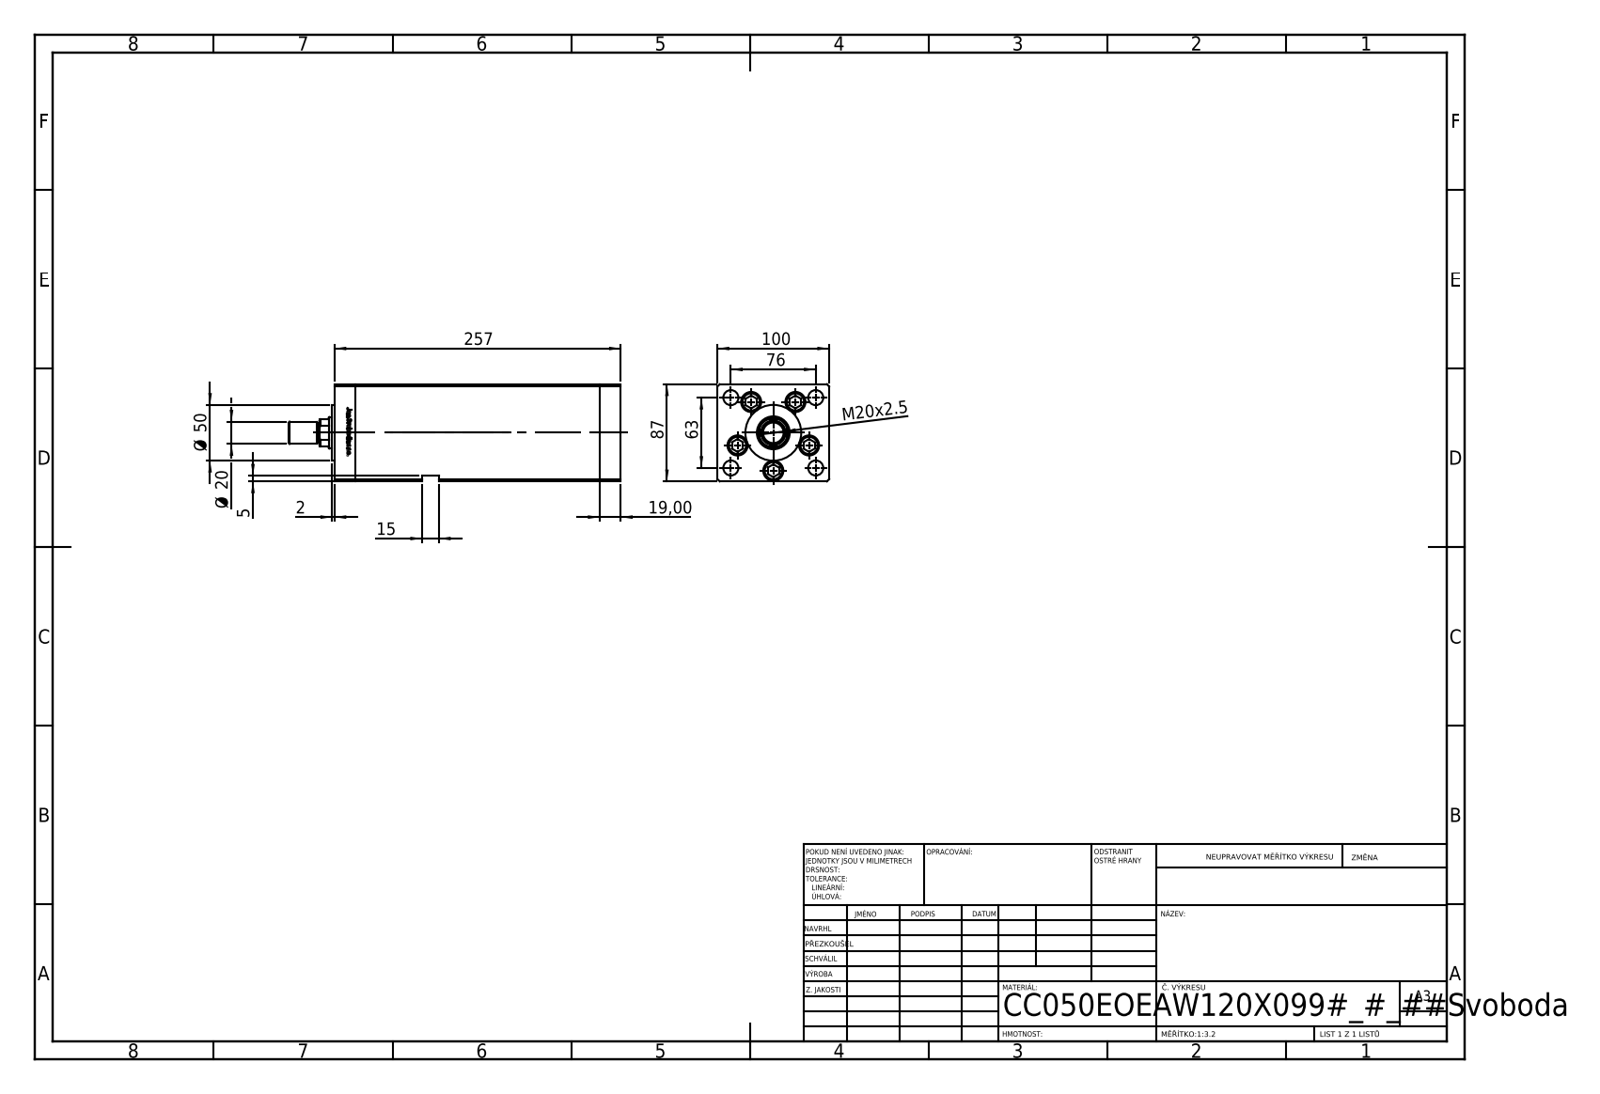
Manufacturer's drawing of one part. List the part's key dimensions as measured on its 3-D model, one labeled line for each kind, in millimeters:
Part name (STEP PRODUCT): V220C_FRONT_E; V220C BACK_E; ALLEN BOLT; V220CC_MALE_METRIC (+2 more)
STEP written by: SolidWorks 2019 (CONFIG_CONTROL_DESIGN)
Units: millimetres
Bodies: 15 solids, 1228 faces (479 planar, 169 cylindrical, 580 other)
Overall size (bounding box): 297.5 × 100 × 87
Volume: 1 874 000 mm³ · Surface area: 268 344 mm²
Round holes (diameter × count): ⌀13.5 ×11, ⌀18 ×5, ⌀18.5 ×5, ⌀12.5 ×4, ⌀2 ×2, ⌀13.16 ×2, ⌀28 ×1, ⌀29.5 ×1
Round bosses / shafts (diameter × count): ⌀17 ×5, ⌀8 ×5, ⌀50 ×1, ⌀20 ×1, ⌀18 ×1
Partial cylindrical surfaces — rounded edges, fillets, slot ends (radius × count): R0.93 ×2, R13.5 ×1
Main face-to-face distances: 100, 87, 19, 218.5, 237.5, 256.5, 34.25, 15.25, 203.25, 222.25
Hole centre spacings: 34, 18.59, 39.64, 49.36, 57.95, 21.03, 38.08, 39.27
